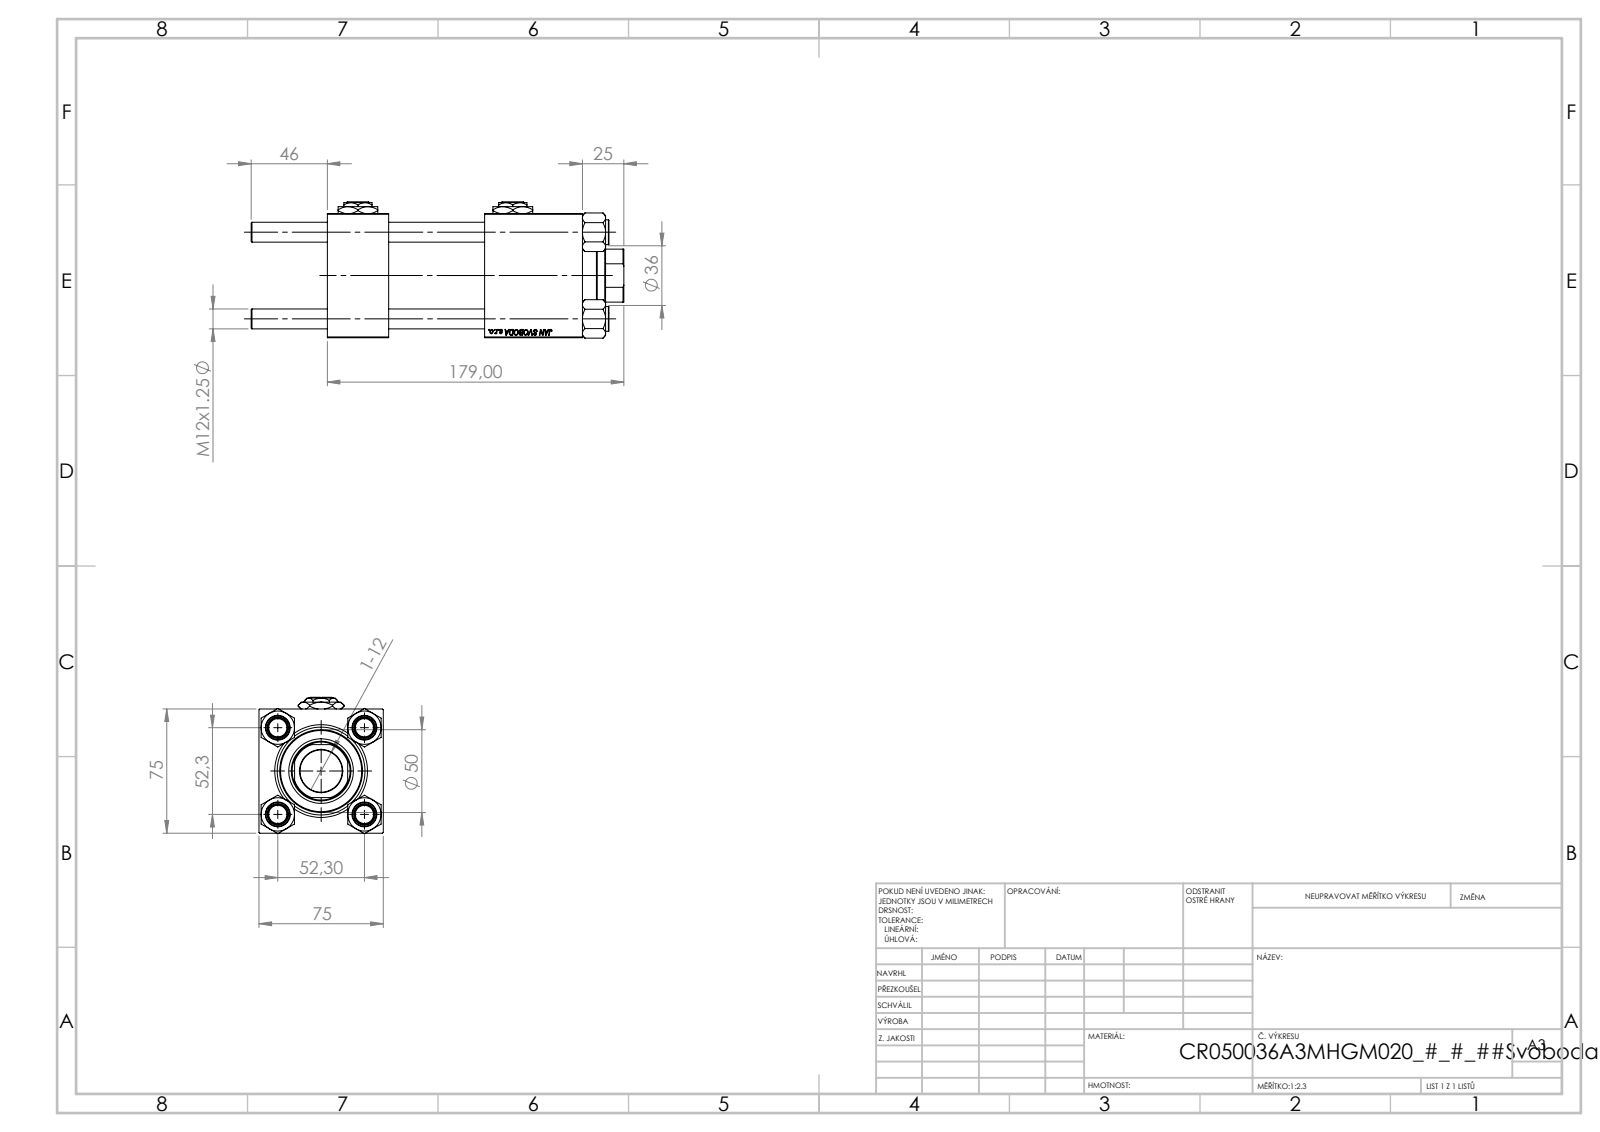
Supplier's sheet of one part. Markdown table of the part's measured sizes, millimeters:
| quantity | value |
| --- | --- |
| part name | Zatka_pro_OIL_PORT; V215CR_BODY_A; CR025_012_A_0_G_A_G_M_020_+#_##_TYCINKA; NUT_M5 (+2 more) |
| STEP written by | SolidWorks 2019 (CONFIG_CONTROL_DESIGN) |
| units | millimeters |
| bodies | 13 solids, 1233 faces (567 planar, 88 cylindrical, 578 other) |
| overall size | 225 × 82.27 × 75 |
| volume | 714 043 mm³ |
| surface area | 176 424 mm² |
| round holes (diameter × count) | 12 × 4, 7 × 2, 20.96 × 2, 30 × 2, 25.5 × 1, 36 × 1, 39 × 1, 41 × 1, 53 × 1 |
| round bosses / shafts (diameter × count) | 15 × 4, 56 × 1, 50 × 1 |
| partial cylindrical surfaces (radius × count) | 17.5 × 1 |
| main face-to-face distances | 75, 37, 95, 154, 117, 59, 58, 74.8, 125.3, 88.3 |
| hole center spacings | 36.98, 52.3, 73.96, 93.5 |
